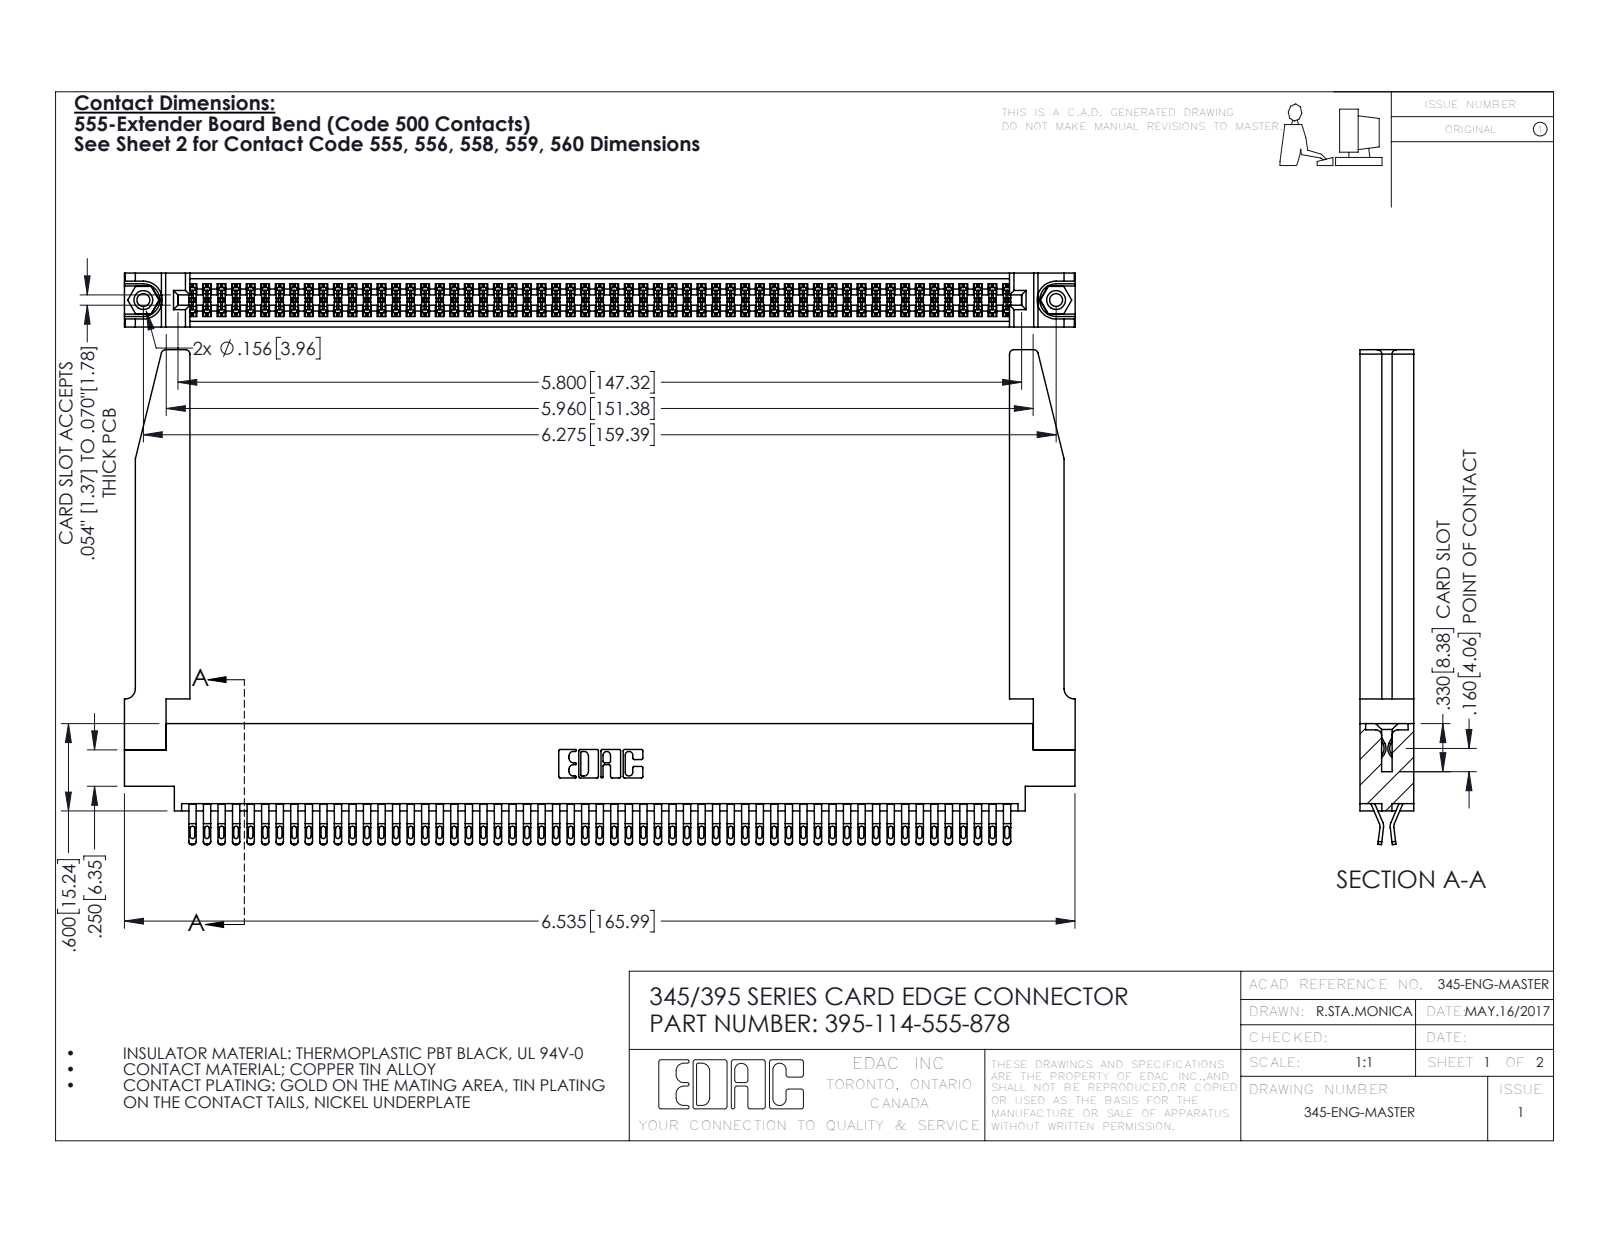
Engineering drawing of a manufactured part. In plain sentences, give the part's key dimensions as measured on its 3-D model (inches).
The part is named "345-220-078_345-220-078; 395-114-555-878; 345-292-001_555 Tail; 345-250-001_345-250-001-102 (+1 more)". Its 3-D file was written by "SolidWorks 2016 (CONFIG_CONTROL_DESIGN)". It is 119 solids with 6748 faces: 3760 planar, 2936 cylindrical and 52 other. Overall it measures 6.536 by 3.402 by 0.37 inches. Its volume is 1.48 cubic inches and its surface area 50.82 square inches. Round holes: 2 of diameter 0.089, 2 of diameter 0.125, 2 of diameter 0.156, 1 of diameter 0.064. Round bosses or shafts: 2 of diameter 0.155. Partial cylindrical surfaces (rounded edges, fillets, slot ends): 285 of radius 0.016, 228 of radius 0.02, 171 of radius 0.006, 22 of radius 0.01, 8 of radius 0.03, 6 of radius 0.007, 6 of radius 0.031, 3 of radius 0.026. The main face-to-face distances are 0.072, 0.37, 0.298, 0.025, 0.098, 0.272, 0.2, 0.225, 0.175, 0.148. The hole center spacings are 0.27, 6.039, 6.275.
